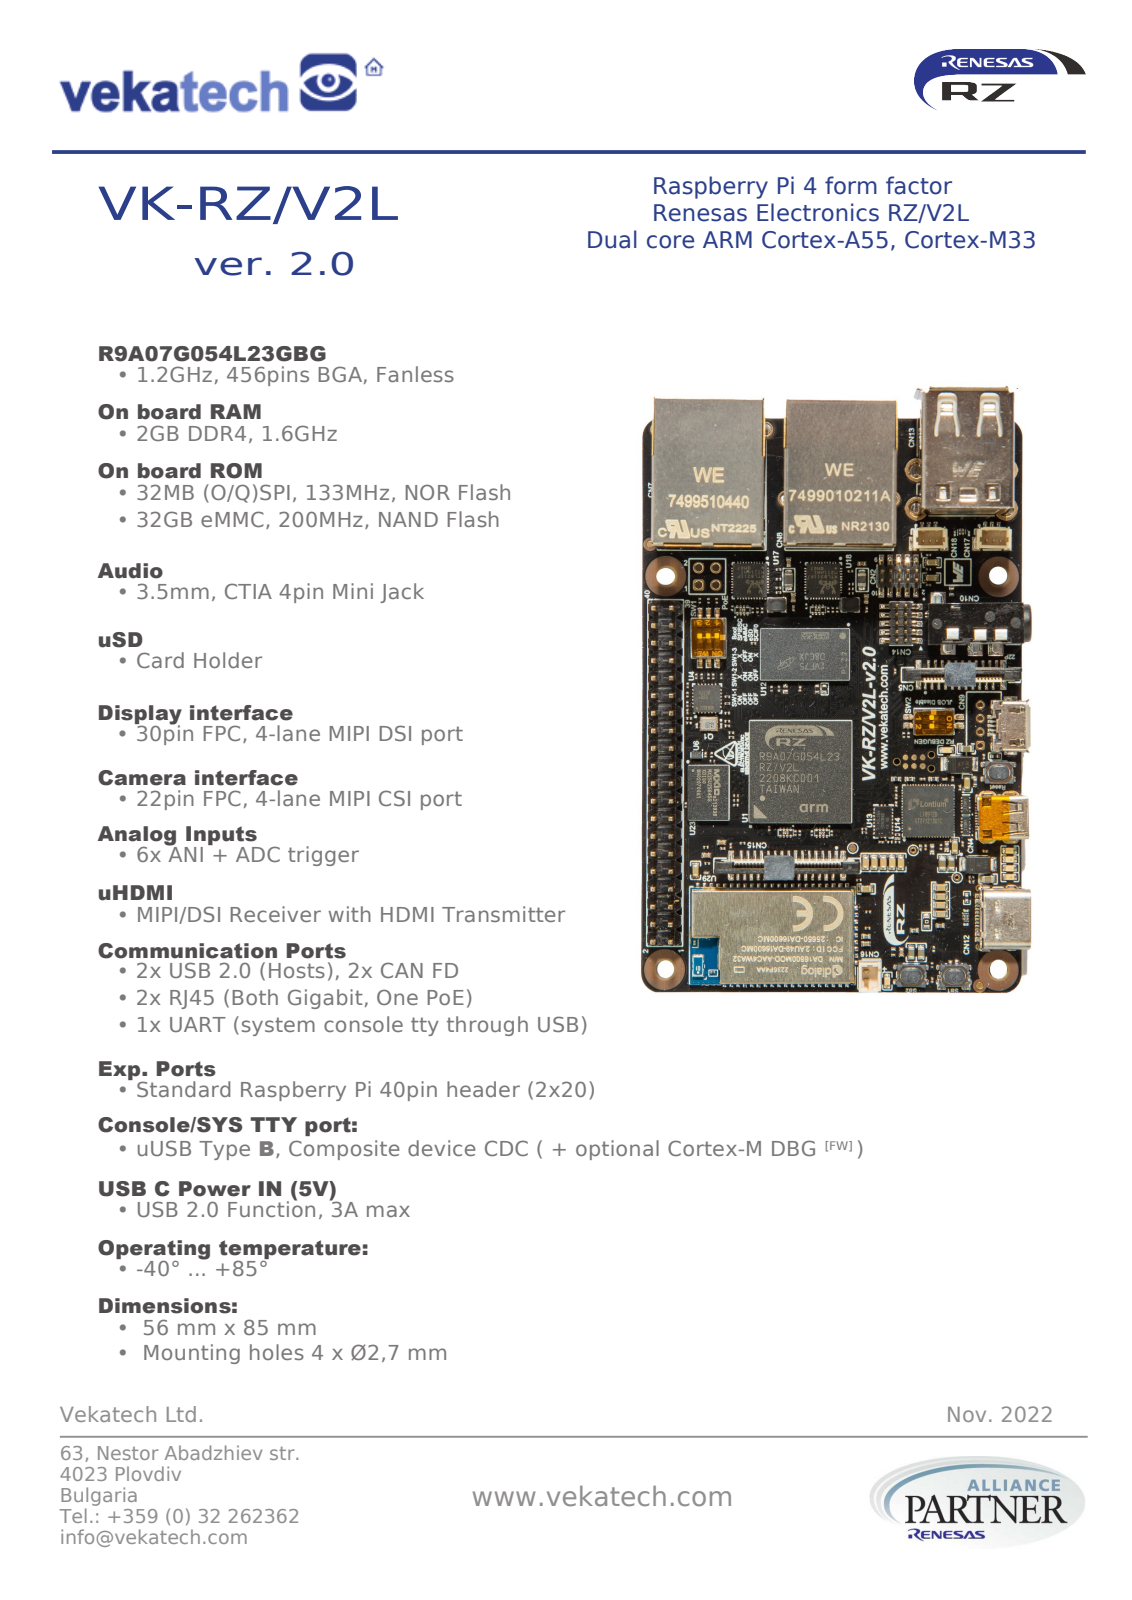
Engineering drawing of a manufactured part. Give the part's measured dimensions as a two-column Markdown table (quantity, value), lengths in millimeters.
| quantity | value |
| --- | --- |
| part name | (Unsaved); Board; R73; R1 (+7 more) |
| STEP written by | Autodesk Translation Framework v12.14.0.127 (AUTOMOTIVE_DESIGN) |
| units | millimeters |
| bodies | 3300 solids, 51676 faces (33709 planar, 10959 cylindrical, 7008 other) |
| overall size | 87.5 × 57.1 × 20.65 |
| volume | 17 560 mm³ |
| surface area | 45 937 mm² |
| round holes (diameter × count) | 1.1 × 46, 0.7 × 39, 0.45 × 24, 1.02 × 18, 0.9 × 10, 0.92 × 8, 0.5 × 7, 0.2 × 4, 0.8 × 4, 1.2 × 4, 1.6 × 4, 2.3 × 4 |
| round bosses / shafts (diameter × count) | 0.25 × 34, 0.45 × 8, 0.6 × 6, 1 × 4, 0.5 × 4, 0.4 × 4, 0.75 × 3, 0.29 × 3 |
| partial cylindrical surfaces (radius × count) | 0.1 × 698, 0.2 × 249, 0.1 × 246, 0.15 × 162, 0.3 × 151, 0.11 × 44, 0.25 × 29, 0.5 × 25 |
| main face-to-face distances | 1.56, 15.7, 0.31, 18.75, 0.39, 15.12, 2.1, 12.96, 15.01, 2.41 |
| hole center spacings | 2.54, 5.08, 7.62, 10.16, 15.24, 2, 12.7, 17.78 |
